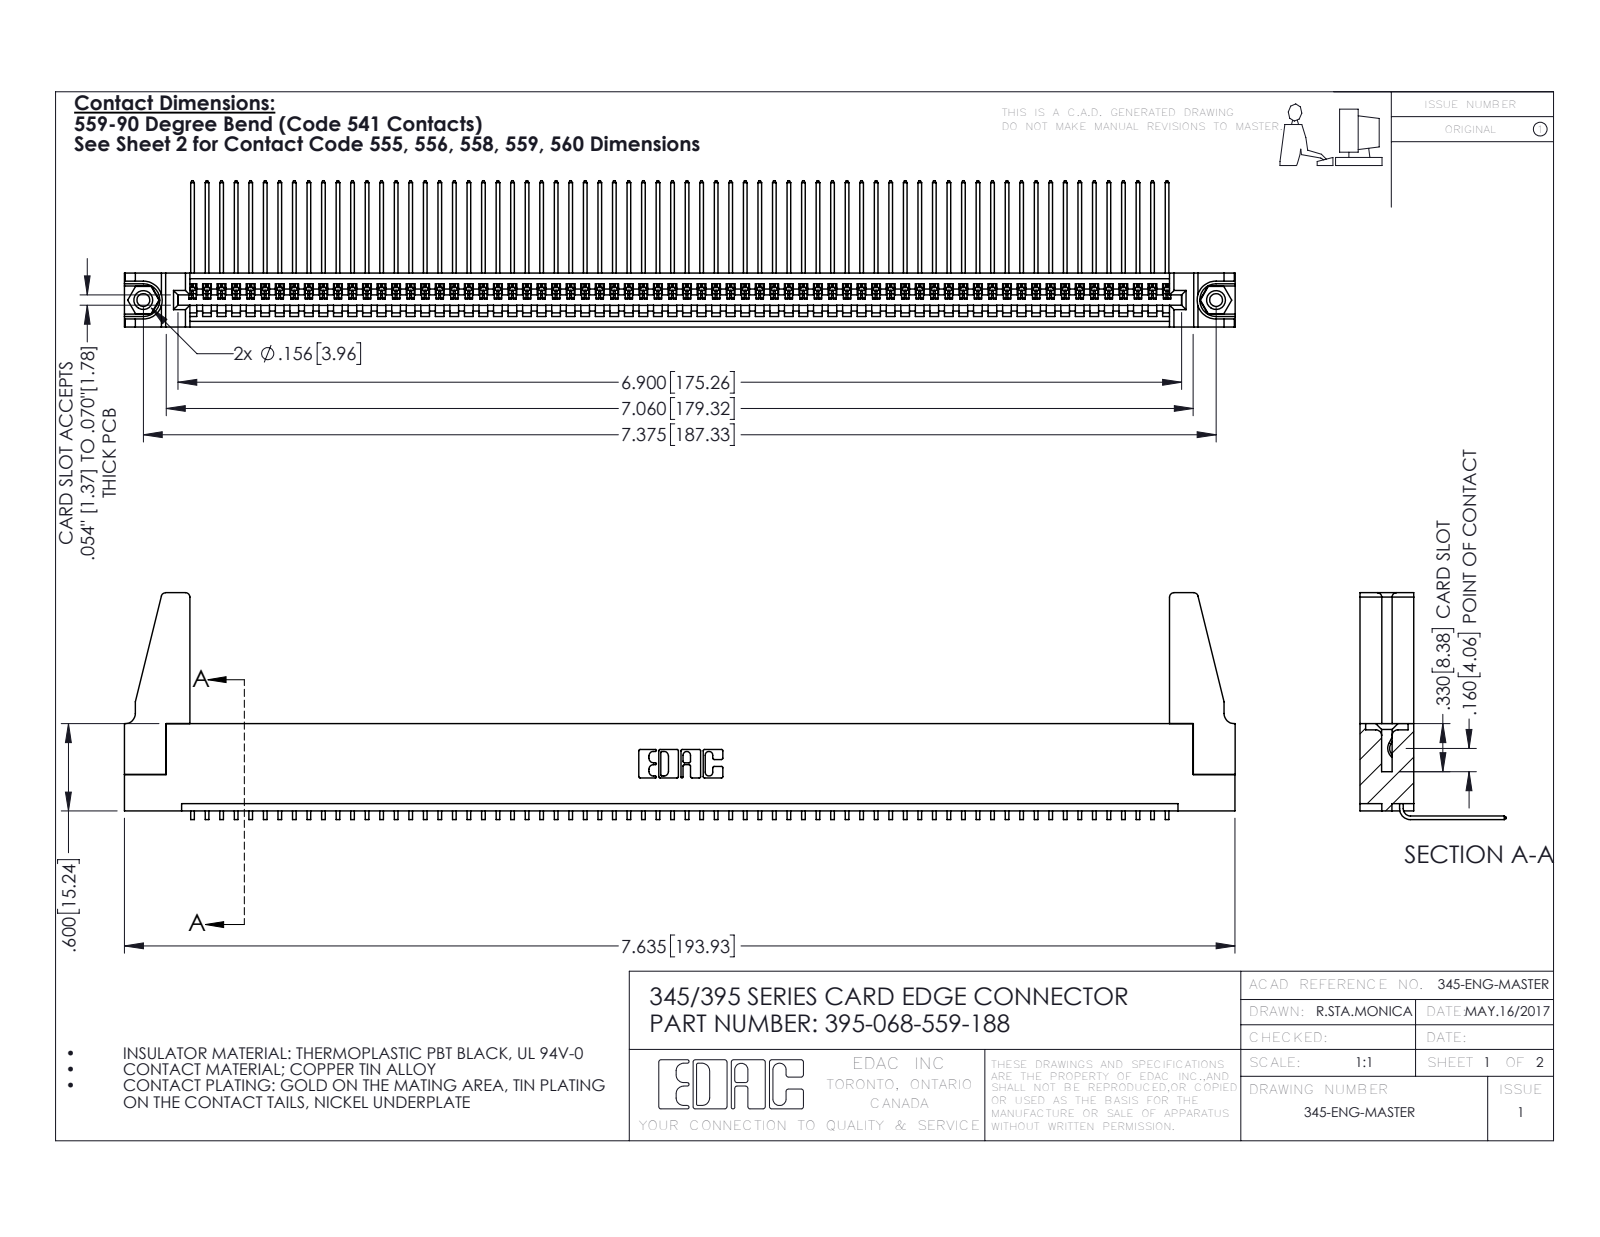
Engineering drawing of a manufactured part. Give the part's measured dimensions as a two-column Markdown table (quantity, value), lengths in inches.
| quantity | value |
| --- | --- |
| part name | 345-220-078_345-220-088; 345 Part_Flush Mounting Lugs - 0.156 Dia-TH; 345-292-001_558 559 Tail - 1; 345-250-001_345-250-001-102 (+1 more) |
| STEP written by | SolidWorks 2016 (CONFIG_CONTROL_DESIGN) |
| units | inches |
| bodies | 73 solids, 4330 faces (3008 planar, 1306 cylindrical, 16 other) |
| overall size | 7.636 × 1.559 × 1.005 |
| volume | 1.349 in³ |
| surface area | 46.31 in² |
| round holes (diameter × count) | 0.089 × 2, 0.125 × 2, 0.156 × 2, 0.064 × 1 |
| round bosses / shafts (diameter × count) | 0.155 × 2 |
| partial cylindrical surfaces (radius × count) | 0.006 × 136, 0.01 × 22, 0.03 × 8, 0.007 × 6, 0.031 × 6, 0.026 × 3, 0.031 × 2, 0.04 × 2 |
| main face-to-face distances | 0.072, 0.298, 0.37, 0.2, 0.098, 0.272, 0.025, 0.225, 0.149, 0.072 |
| hole center spacings | 0.27, 7.139, 7.375 |
